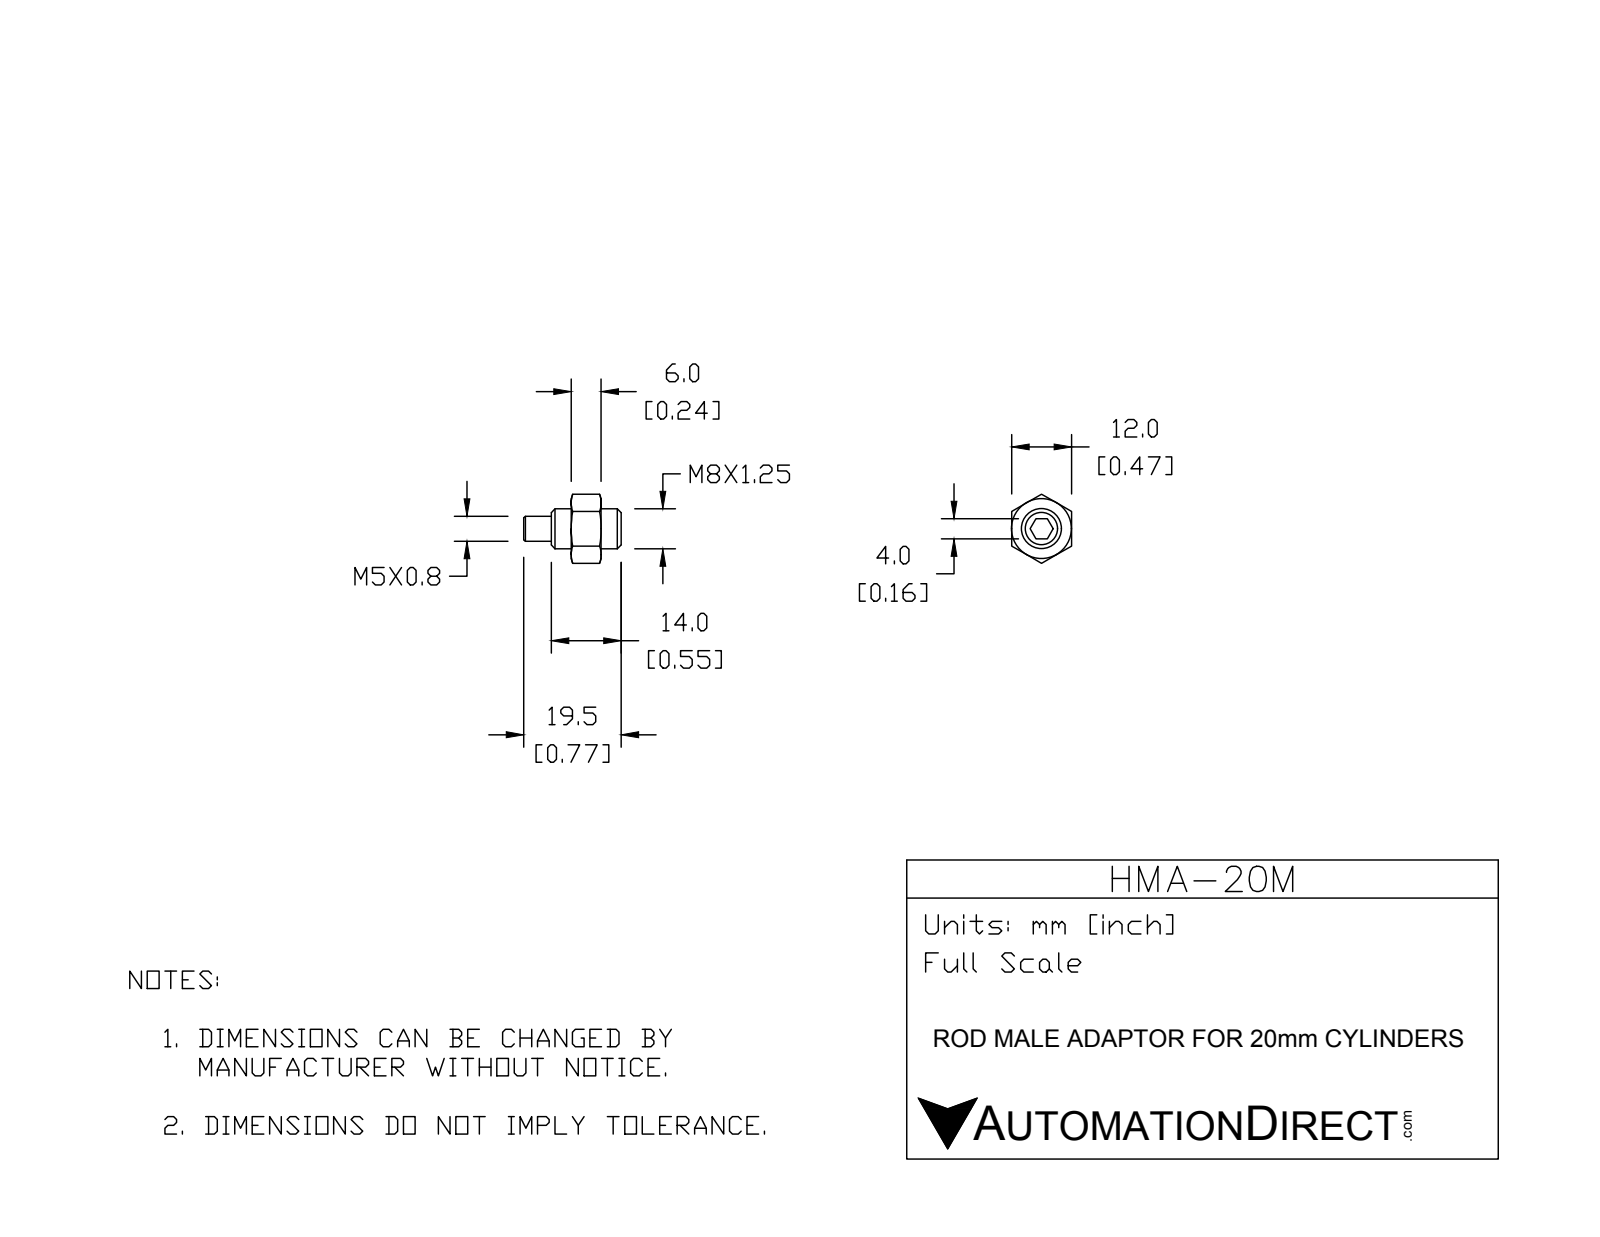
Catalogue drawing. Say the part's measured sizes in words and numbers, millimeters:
The part is named "HMA-20M". Its 3-D file was written by "SolidWorks 2015 (CONFIG_CONTROL_DESIGN)". It is 2 solids with 44 faces: 18 planar, 6 cylindrical and 20 other. Overall it measures 19.5 by 13.86 by 12 millimeters. Its volume is 1 193 cubic millimeters and its surface area 1 102 square millimeters. Round holes: 1 of diameter 8. Round bosses or shafts: 1 of diameter 5. The main face-to-face distances are 12, 6, 4, 10, 19.5, 15.5, 9.5, 3.5, 0.5, 6.5.
